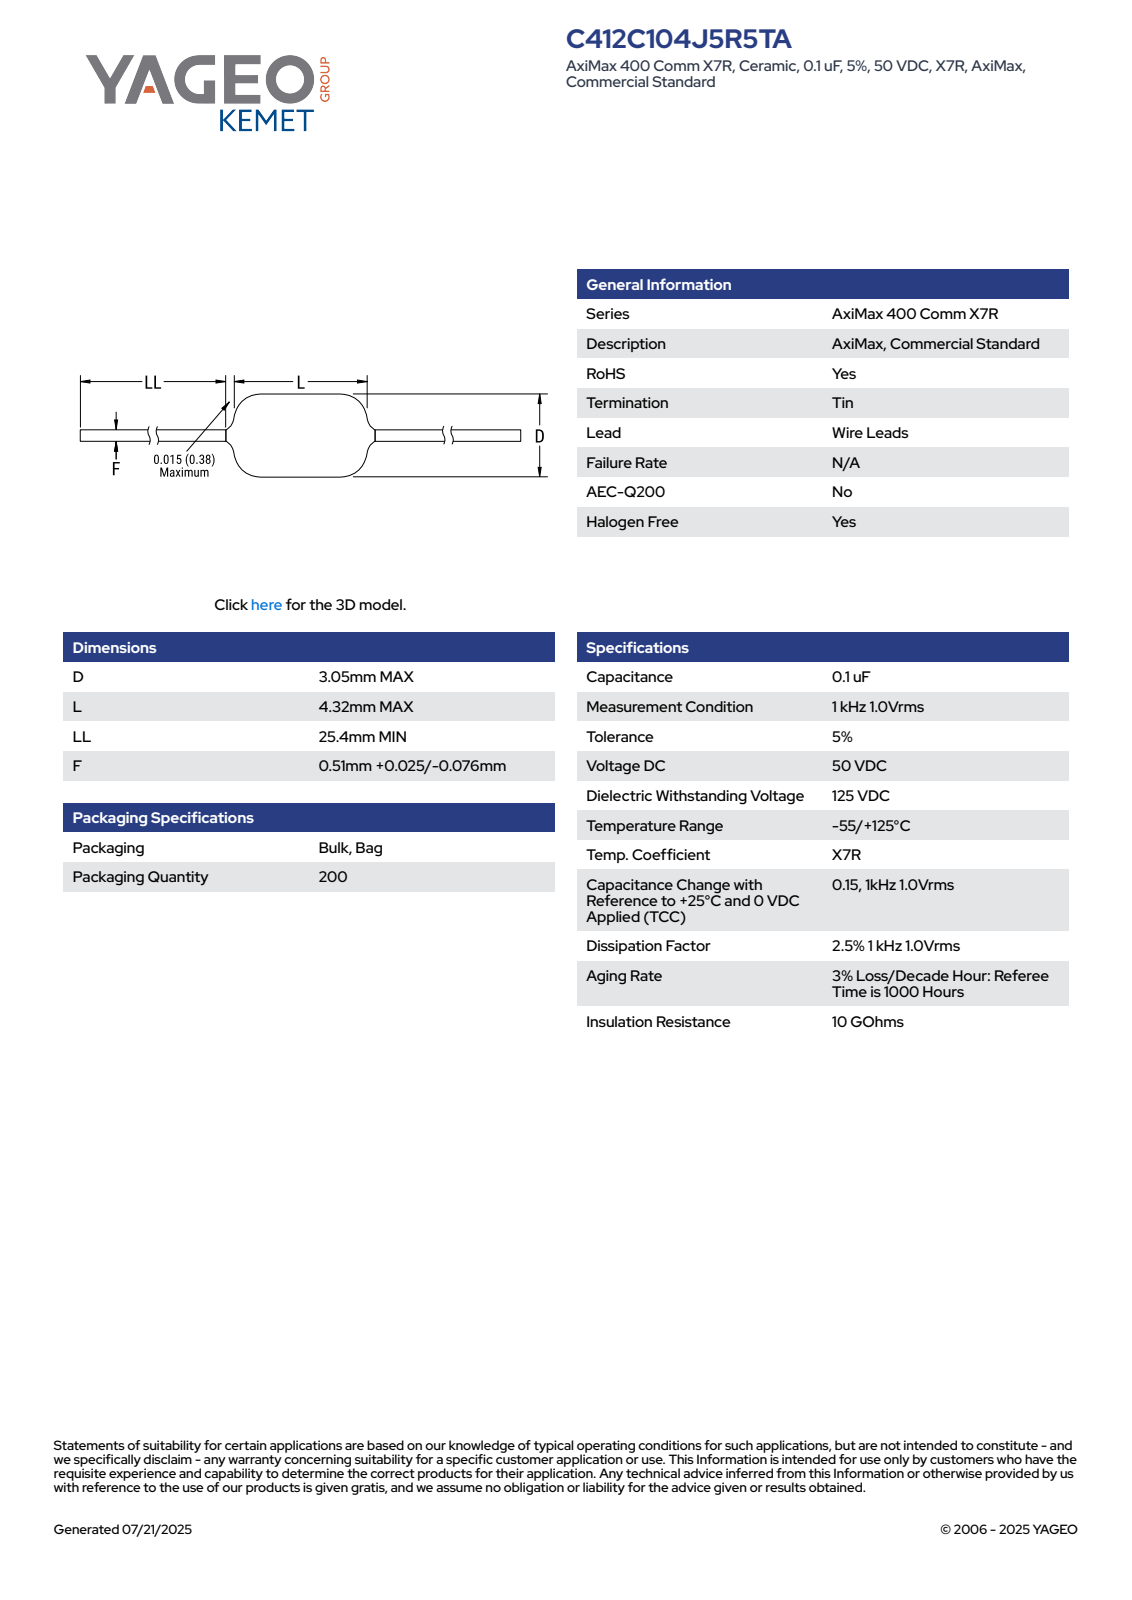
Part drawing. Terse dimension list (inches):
name: CCA_ACST_C412_D3.05L4.32LL25.4F0.535
written by: SolidWorks 2014 (AUTOMOTIVE_DESIGN)
unit: in
bodies: 1 solid, 74 faces (26 planar, 9 cylindrical, 39 other)
size: 2.2 × 0.12 × 0.12
volume: 0.003 in³; area: 0.212 in²
bosses: 1× ⌀0.12, 1× ⌀0.021
rounds: 1× R0.059
face distances: 0.17, 1.015, 1.185, 2.2
